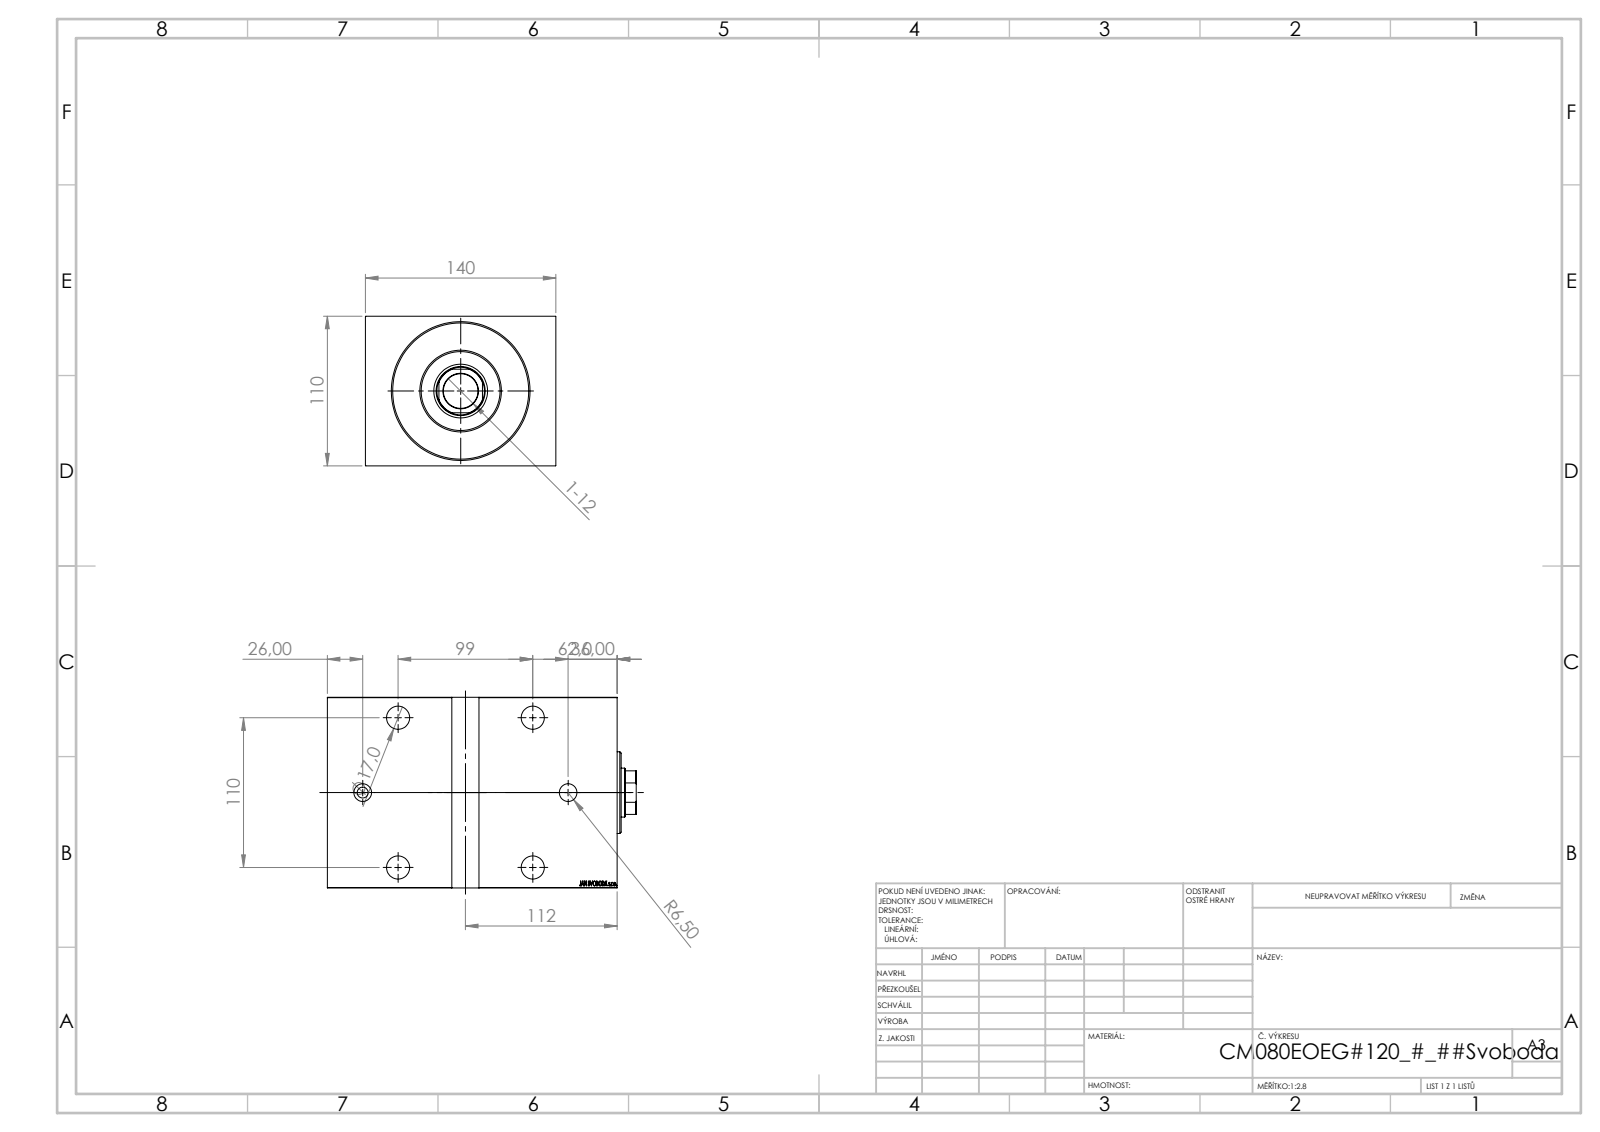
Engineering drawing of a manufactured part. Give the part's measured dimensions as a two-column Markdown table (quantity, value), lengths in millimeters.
| quantity | value |
| --- | --- |
| part name | V450CM_E_Body; V450CM_VC_B; V450CM_E_VCP |
| STEP written by | SolidWorks 2019 (CONFIG_CONTROL_DESIGN) |
| units | millimeters |
| bodies | 3 solids, 849 faces (409 planar, 46 cylindrical, 394 other) |
| overall size | 227 × 140 × 110 |
| volume | 2 671 000 mm³ |
| surface area | 276 131 mm² |
| round holes (diameter × count) | 17 × 4, 25 × 4, 13 × 2, 25.5 × 1, 36 × 1, 39.5 × 1, 80 × 1, 100 × 1 |
| round bosses / shafts (diameter × count) | 82 × 1, 60 × 1, 8 × 1 |
| partial cylindrical surfaces (radius × count) | 17.5 × 1 |
| main face-to-face distances | 110, 140, 213, 21, 192, 5, 208, 187, 79, 196.4 |
| hole center spacings | 60.84, 136.57, 99, 110, 147.99, 151 |
